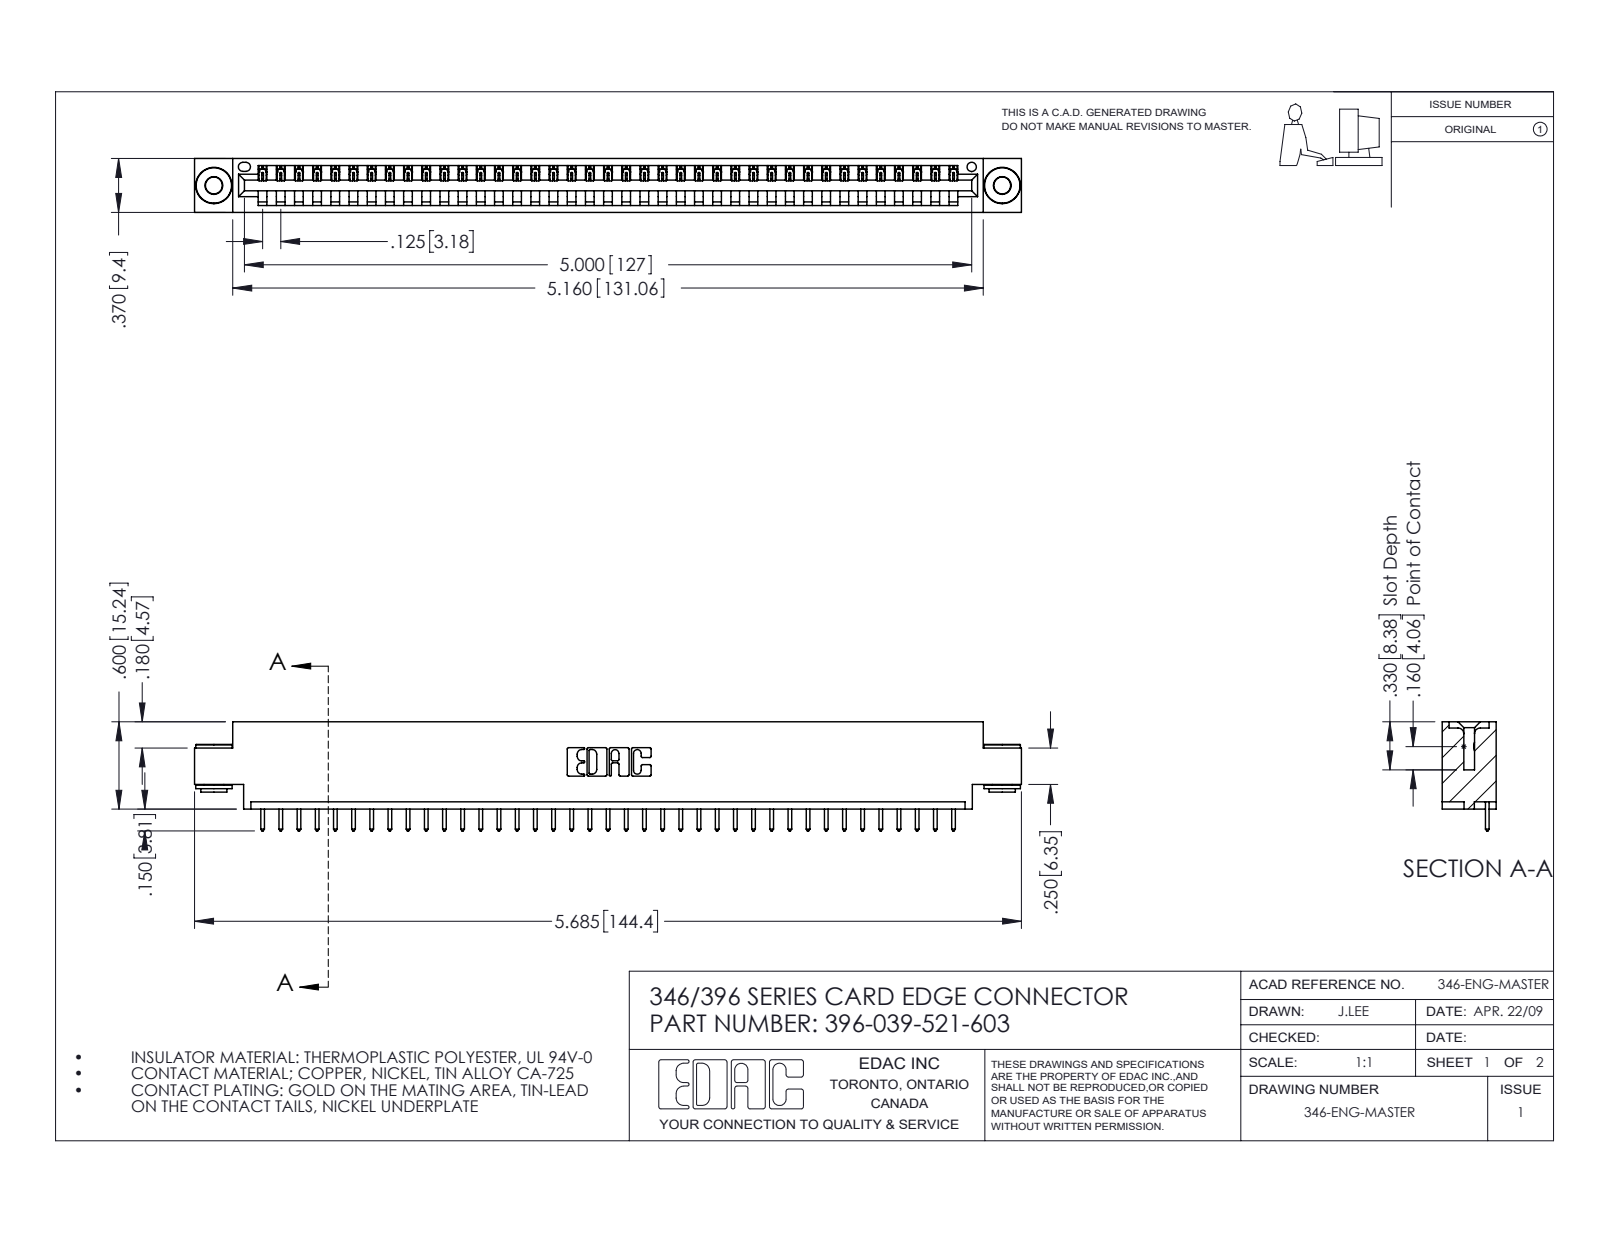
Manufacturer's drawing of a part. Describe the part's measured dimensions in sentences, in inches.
The part is named "345-292-001_345-293-121; 346 Part_0.170 Offset - 0.156 Dia-TH; 396-039-521-603; 345-250-002_345-250-002-102". Its 3-D file was written by "SolidWorks 2016 (CONFIG_CONTROL_DESIGN)". It is 42 solids with 2426 faces: 1650 planar, 768 cylindrical and 8 other. Overall it measures 5.685 by 0.75 by 0.37 inches. Its volume is 0.827 cubic inches and its surface area 26.11 square inches. Round holes: 2 of diameter 0.116, 2 of diameter 0.156, 1 of diameter 0.064. Round bosses or shafts: 2 of diameter 0.25, 2 of diameter 0.18, 2 of diameter 0.136. Partial cylindrical surfaces (rounded edges, fillets, slot ends): 78 of radius 0.006, 78 of radius 0.01, 22 of radius 0.01, 6 of radius 0.007, 6 of radius 0.031, 3 of radius 0.026, 2 of radius 0.031, 2 of radius 0.04. The main face-to-face distances are 0.048, 0.322, 0.37, 0.25, 0.025, 0.072, 0.298, 0.148, 0.222, 0.1. The hole center spacings are 0.246, 5.211, 5.42.
